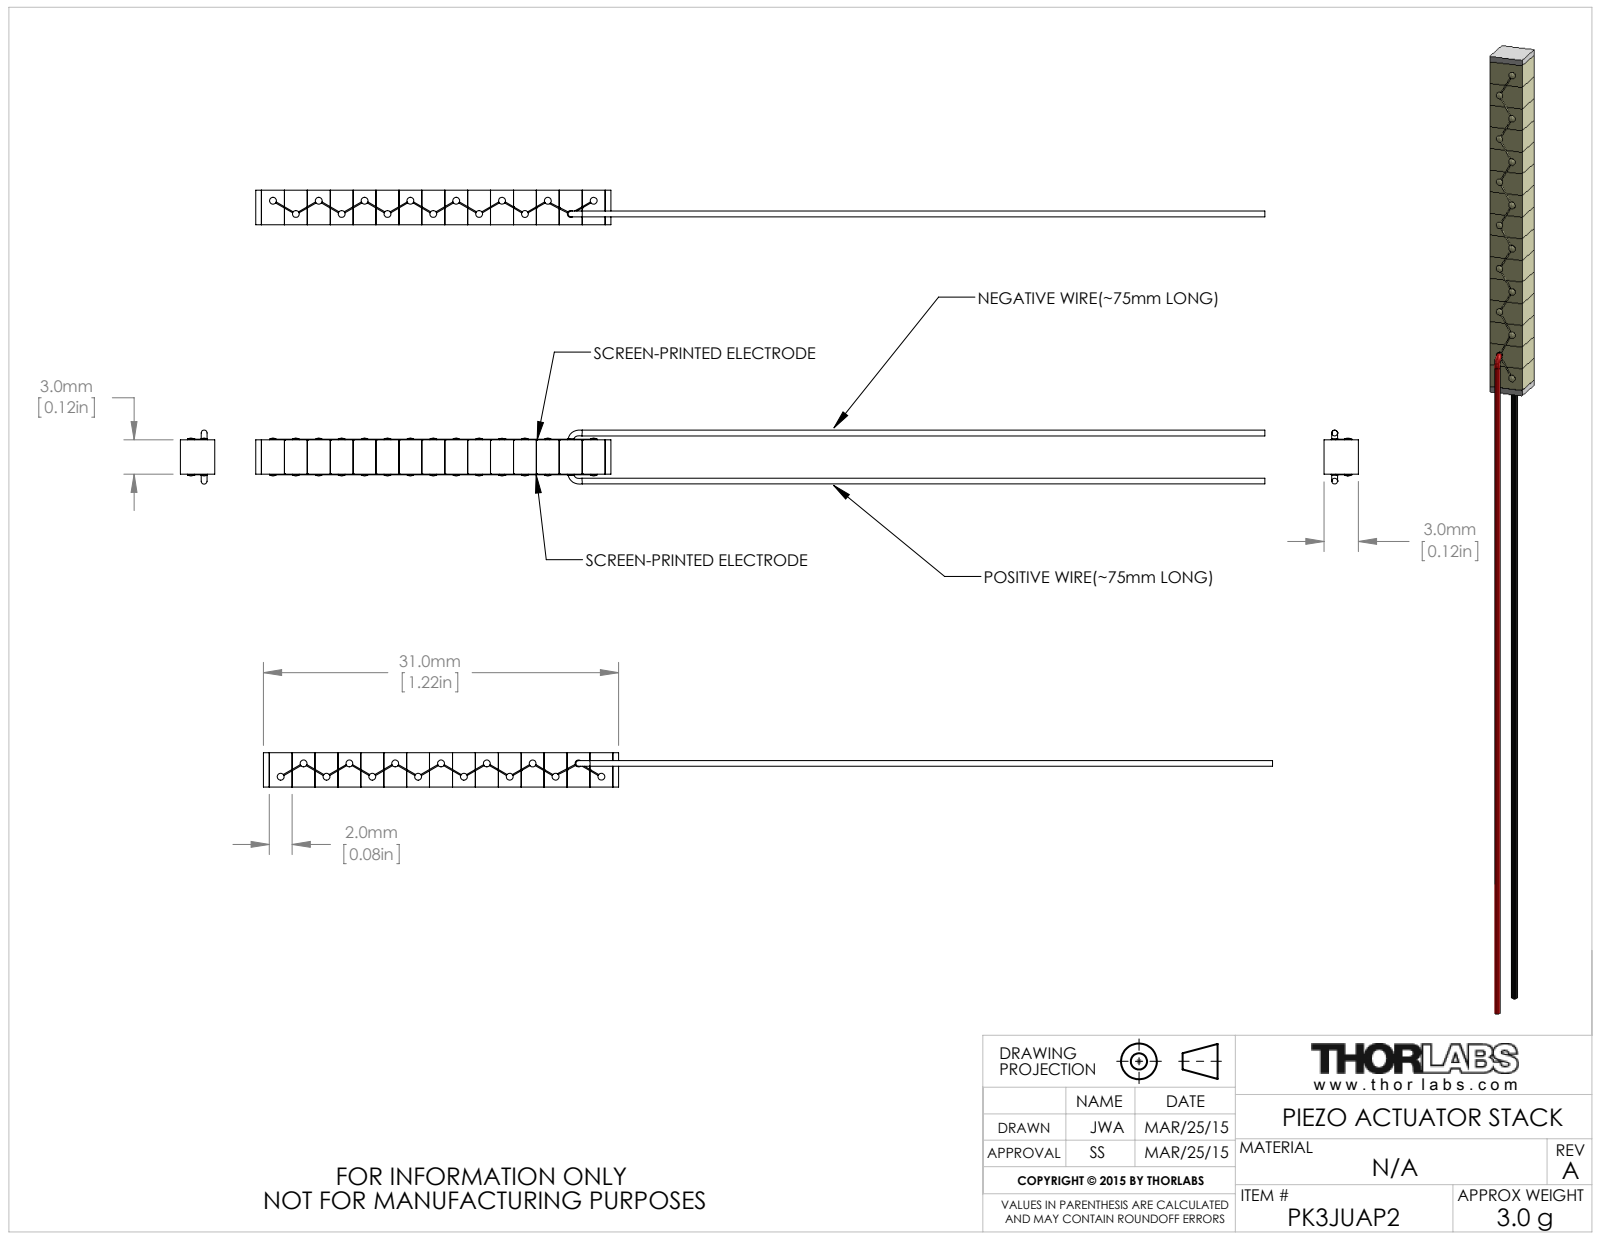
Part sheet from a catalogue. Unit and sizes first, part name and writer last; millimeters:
Units: millimetres
Overall size (bounding box): 88.1 × 4.72 × 3
Round bosses / shafts (diameter × count): ⌀0.6 ×15
Main face-to-face distances: 2, 4, 6, 8, 10, 3, 12, 14, 16, 18
Volume: 304 mm³ · Surface area: 893 mm²
Bodies: 20 solids, 313 faces (121 planar, 126 cylindrical, 66 other)
Part name (STEP PRODUCT): CTN002741
STEP written by: SolidWorks 2014 (AUTOMOTIVE_DESIGN)
